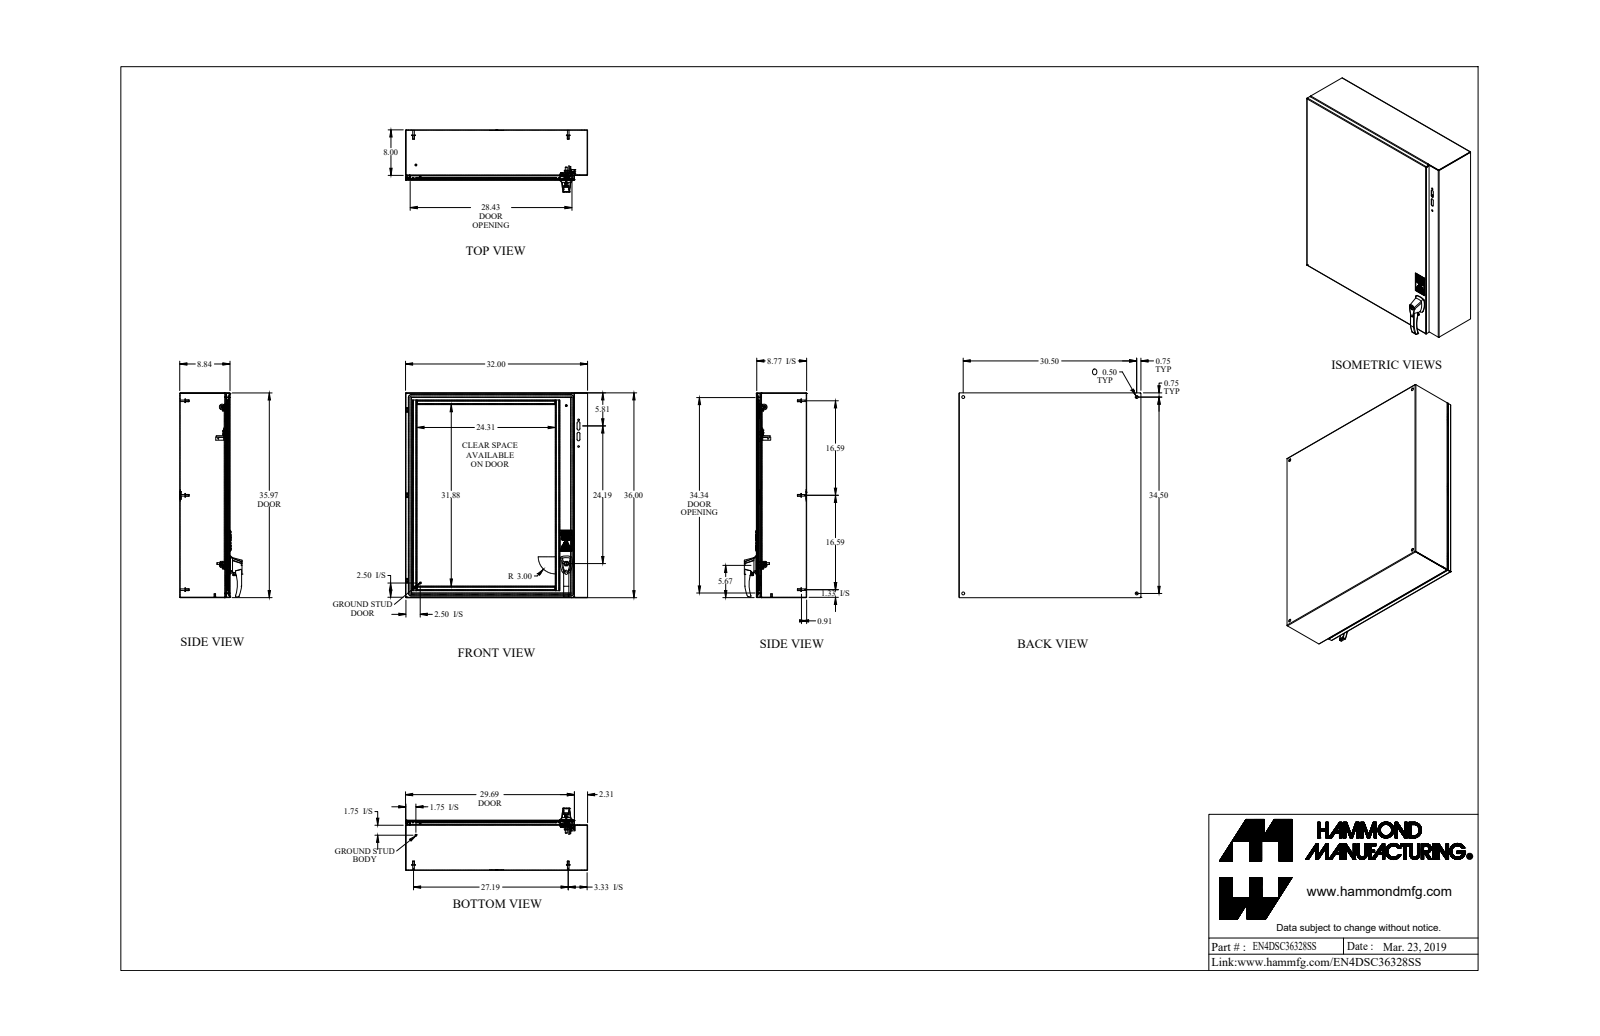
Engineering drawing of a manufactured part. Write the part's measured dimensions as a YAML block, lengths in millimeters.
part_name: "EN4DSC36328SS"
step_written_by: "SolidWorks 2019 (AUTOMOTIVE_DESIGN)"
units: millimeters
bodies: {solids: 55, faces: 1145, planar: 617, cylindrical: 365, other: 163}
overall_size: [914.4, 812.8, 278.18]
volume: 4319000
surface_area: 5289000
round_holes:
  - {diameter: 4.47, count: 4}
  - {diameter: 3.97, count: 2}
  - {diameter: 4.39, count: 2}
  - {diameter: 5.46, count: 2}
  - {diameter: 6.35, count: 2}
  - {diameter: 6.73, count: 2}
  - {diameter: 7.14, count: 2}
  - {diameter: 10.49, count: 2}
  - {diameter: 4.37, count: 1}
  - {diameter: 4.98, count: 1}
  - {diameter: 5.92, count: 1}
  - {diameter: 6.1, count: 1}
round_bosses_or_shafts:
  - {diameter: 6.35, count: 7}
  - {diameter: 15.87, count: 6}
  - {diameter: 7.94, count: 6}
  - {diameter: 6.86, count: 6}
  - {diameter: 9.53, count: 4}
  - {diameter: 3.97, count: 4}
  - {diameter: 25.4, count: 2}
  - {diameter: 12.7, count: 2}
partial_cylinders:
  - {radius: 2, count: 28}
  - {radius: 1.09, count: 24}
  - {radius: 2.06, count: 24}
  - {radius: 0.55, count: 16}
  - {radius: 6.35, count: 14}
  - {radius: 3.17, count: 11}
  - {radius: 3.45, count: 8}
  - {radius: 0.14, count: 6}
face_to_face_distances: [1.45, 221.18, 222.63, 1.83, 223.01, 224.46, 811.35, 912.95, 201.75, 812.8]
hole_center_spacings: [704.85, 28.2, 13.21, 19.05, 20.75, 25.2, 25.51, 28.93]
